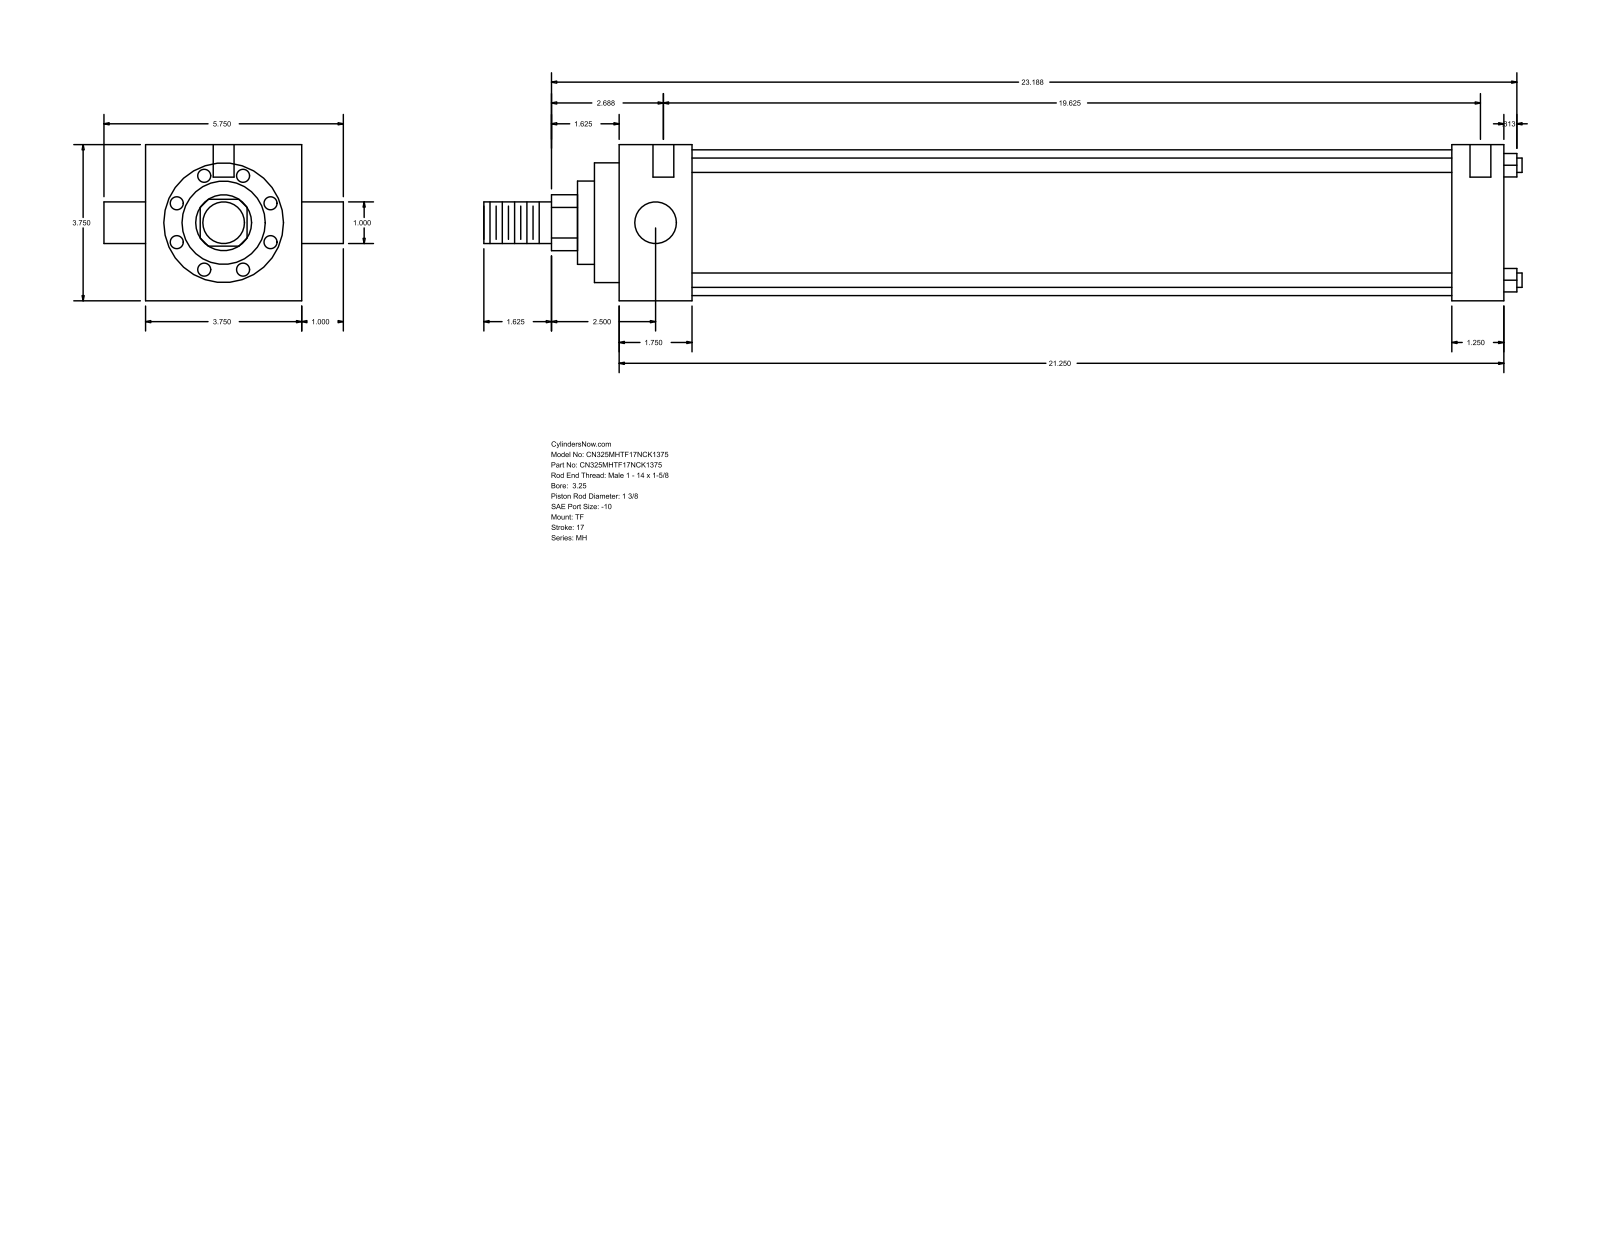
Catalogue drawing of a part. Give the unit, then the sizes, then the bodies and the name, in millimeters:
Units: millimetres
Overall size (bounding box): 633.41 × 146.05 × 95.25
Round holes (diameter × count): ⌀5.56 ×3, ⌀12.7 ×2
Round bosses / shafts (diameter × count): ⌀8.76 ×4, ⌀25.4 ×2, ⌀88.9 ×1, ⌀73.03 ×1, ⌀50.8 ×1, ⌀34.92 ×1
Partial cylindrical surfaces — rounded edges, fillets, slot ends (radius × count): R17.06 ×1
Main face-to-face distances: 95.24, 539.75, 44.45, 508, 463.55, 495.3, 31.75, 15.08, 59.53, 523.08
Hole centre spacings: 1.59, 4.76, 498.48, 500.07, 503.24, 504.83
Bodies: 0 solids, 86 faces (61 planar, 25 cylindrical, 0 other)
Part name (STEP PRODUCT): MH_TF__0325_1.375
STEP written by: GSSL Pune (CONFIG_CONTROL_DESIGN)
